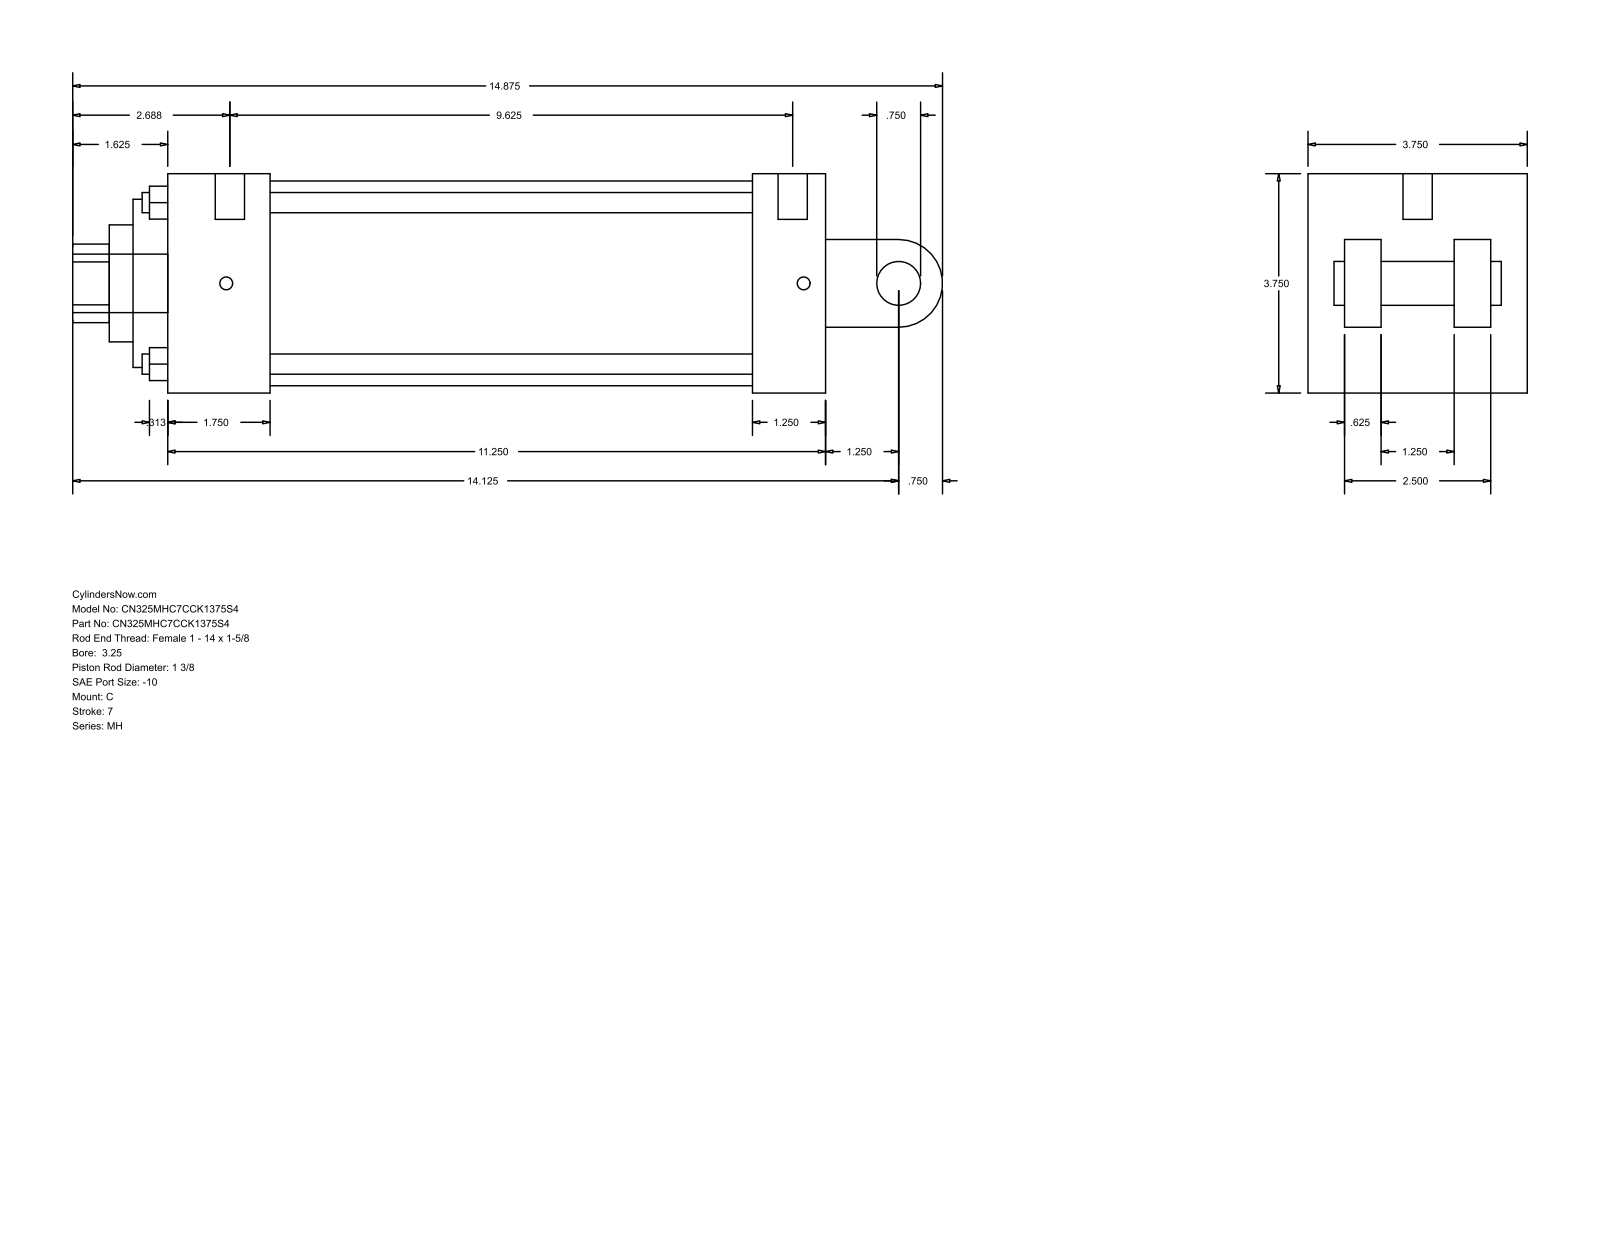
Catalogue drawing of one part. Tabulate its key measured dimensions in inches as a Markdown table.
| quantity | value |
| --- | --- |
| part name | MH_C__0325_1.375 |
| STEP written by | GSSL Pune (CONFIG_CONTROL_DESIGN) |
| units | inches |
| bodies | 0 solids, 101 faces (71 planar, 30 cylindrical, 0 other) |
| overall size | 14.875 × 3.75 × 3.75 |
| round holes (diameter × count) | 0.345 × 4, 0.219 × 2, 0.5 × 1, 1.375 × 1, 2 × 1, 2.875 × 1, 3.5 × 1 |
| round bosses / shafts (diameter × count) | 0.219 × 2, 1 × 1, 0.75 × 1, 0.5 × 1 |
| partial cylindrical surfaces (radius × count) | 0.672 × 1, 0.75 × 1 |
| main face-to-face distances | 3.75, 0.625, 11.25, 2.5, 3.125, 1.25, 1.875, 1.75, 10, 8.25 |
| hole center spacings | 1.952, 2.76, 3.903, 0.187 |
